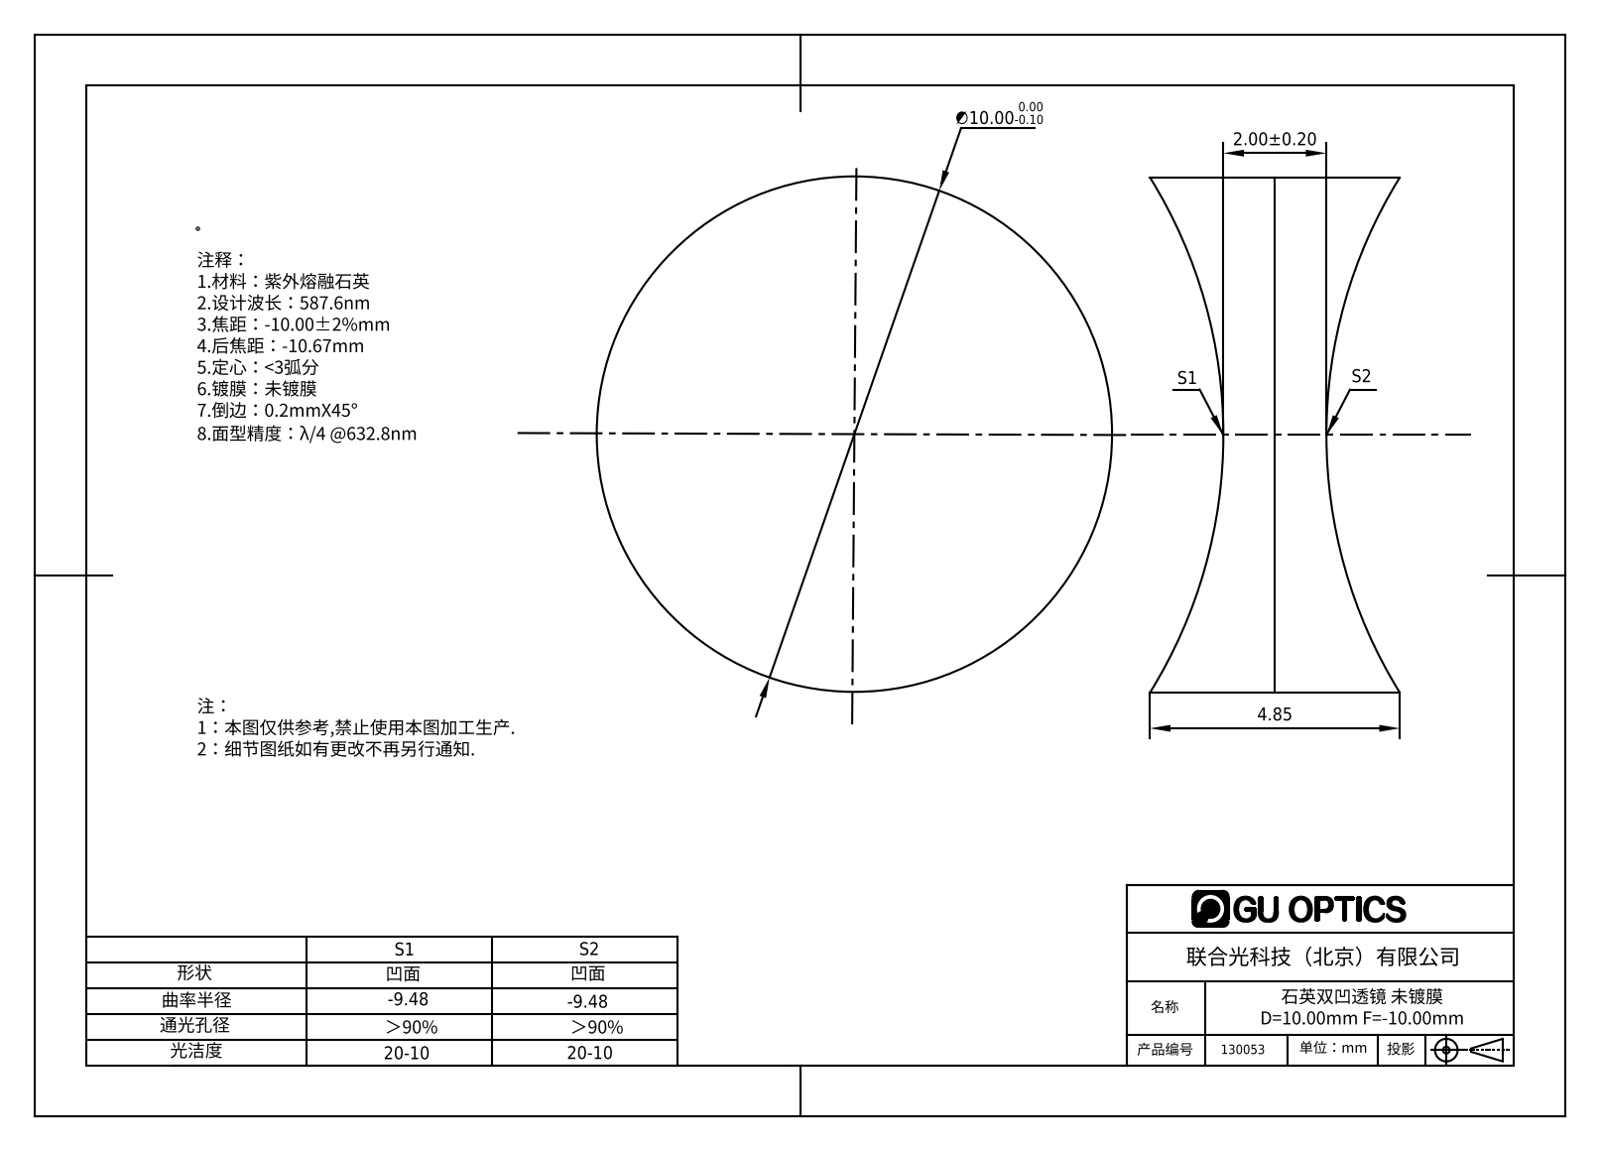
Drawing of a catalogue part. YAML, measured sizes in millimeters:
part_name: "130053"
step_written_by: "SolidWorks 2016 (AUTOMOTIVE_DESIGN)"
units: millimeters
bodies: {solids: 1, faces: 6, planar: 0, cylindrical: 2, other: 4}
overall_size: [10, 10, 4.85]
volume: 266
surface_area: 322
round_bosses_or_shafts:
  - {diameter: 10, count: 1}
